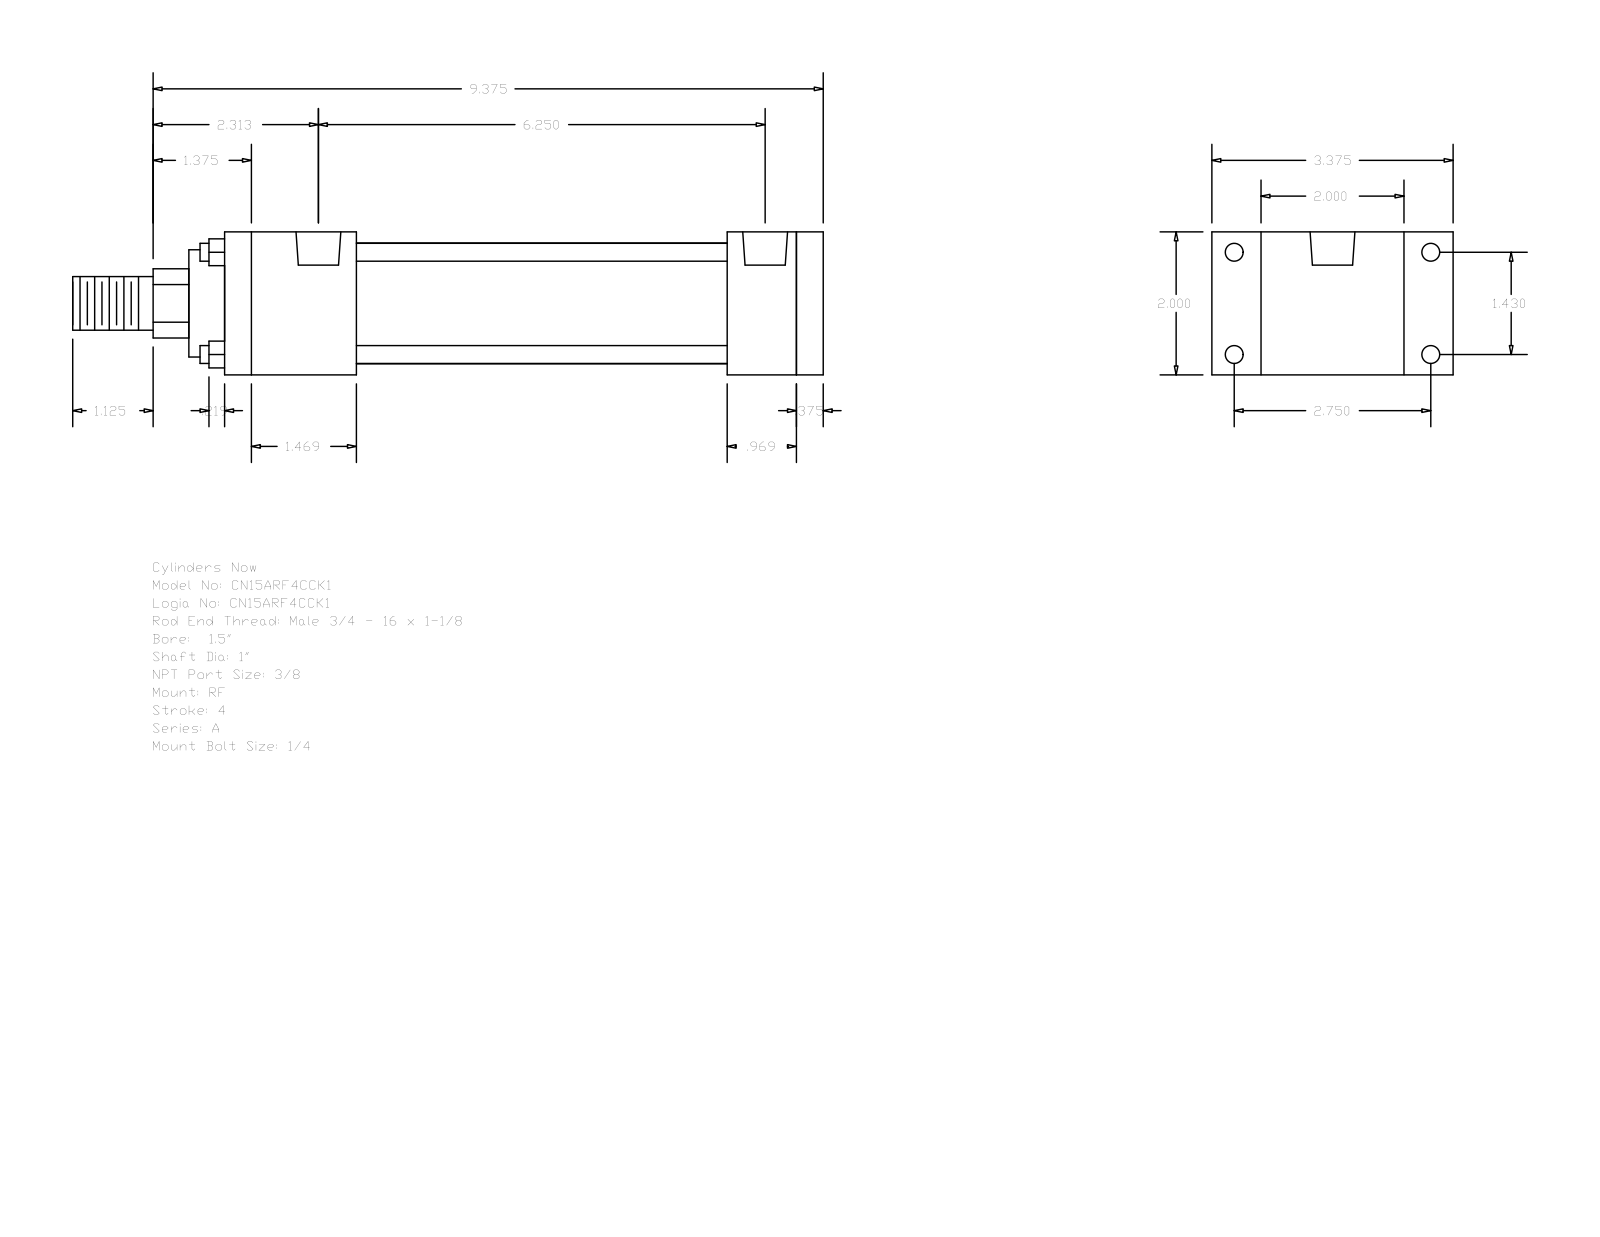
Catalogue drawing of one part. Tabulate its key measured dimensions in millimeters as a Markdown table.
| quantity | value |
| --- | --- |
| part name | A_RF__0150_1 |
| STEP written by | GSSL Pune (CONFIG_CONTROL_DESIGN) |
| units | millimeters |
| bodies | 0 solids, 92 faces (64 planar, 28 cylindrical, 0 other) |
| overall size | 266.7 × 85.72 × 50.8 |
| round holes (diameter × count) | 5.56 × 4, 6.35 × 4, 15.93 × 2 |
| round bosses / shafts (diameter × count) | 6.35 × 4, 42.93 × 1, 38.1 × 1, 25.4 × 1, 19.05 × 1 |
| partial cylindrical surfaces (radius × count) | 12.29 × 1 |
| main face-to-face distances | 50.8, 9.52, 203.2, 212.72, 178.59, 24.61, 34.13, 46.83, 131.76, 156.37 |
| hole center spacings | 3.97, 36.32, 69.84, 78.72, 150.81, 154.78, 158.75 |
